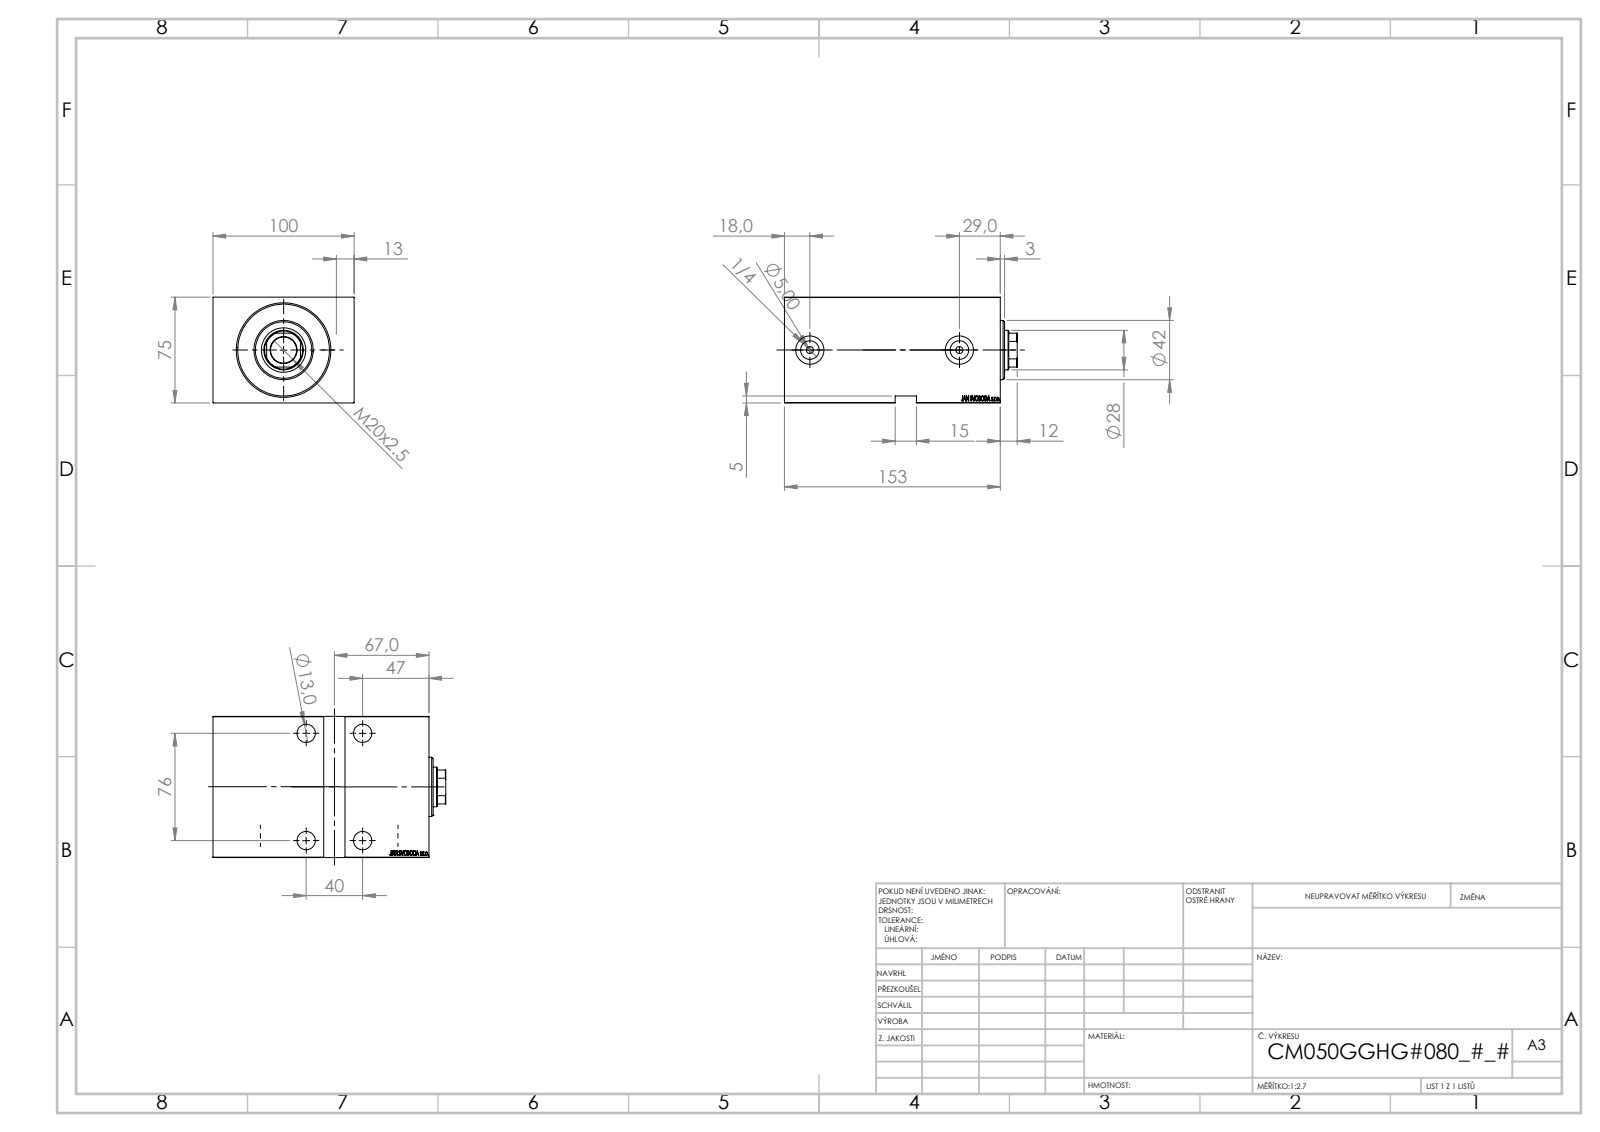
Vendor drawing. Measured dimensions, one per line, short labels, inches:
name: V450CM_G_Body; Zatka_OIL_PORT; V450CM_VC_G; V450CM_G_VCP
written by: SolidWorks 2019 (CONFIG_CONTROL_DESIGN)
unit: in
bodies: 5 solids, 894 faces (440 planar, 56 cylindrical, 398 other)
size: 6.496 × 3.937 × 2.953
volume: 59.09 in³; area: 211.8 in²
holes: 4× ⌀0.512, 4× ⌀0.748, 2× ⌀0.197, 2× ⌀0.518, 2× ⌀0.787, 1× ⌀0.728, 1× ⌀1.102, 1× ⌀1.24, 1× ⌀1.969, 1× ⌀2.047, 1× ⌀2.559
bosses: 2× ⌀0.709, 1× ⌀1.654
rounds: 1× R0.531
face distances: 2.953, 3.937, 6.024, 0.197, 0.551, 5.472, 5.276, 5.827, 2.756, 2.402
hole spacings: 1.575, 2.992, 3.381, 4.173
